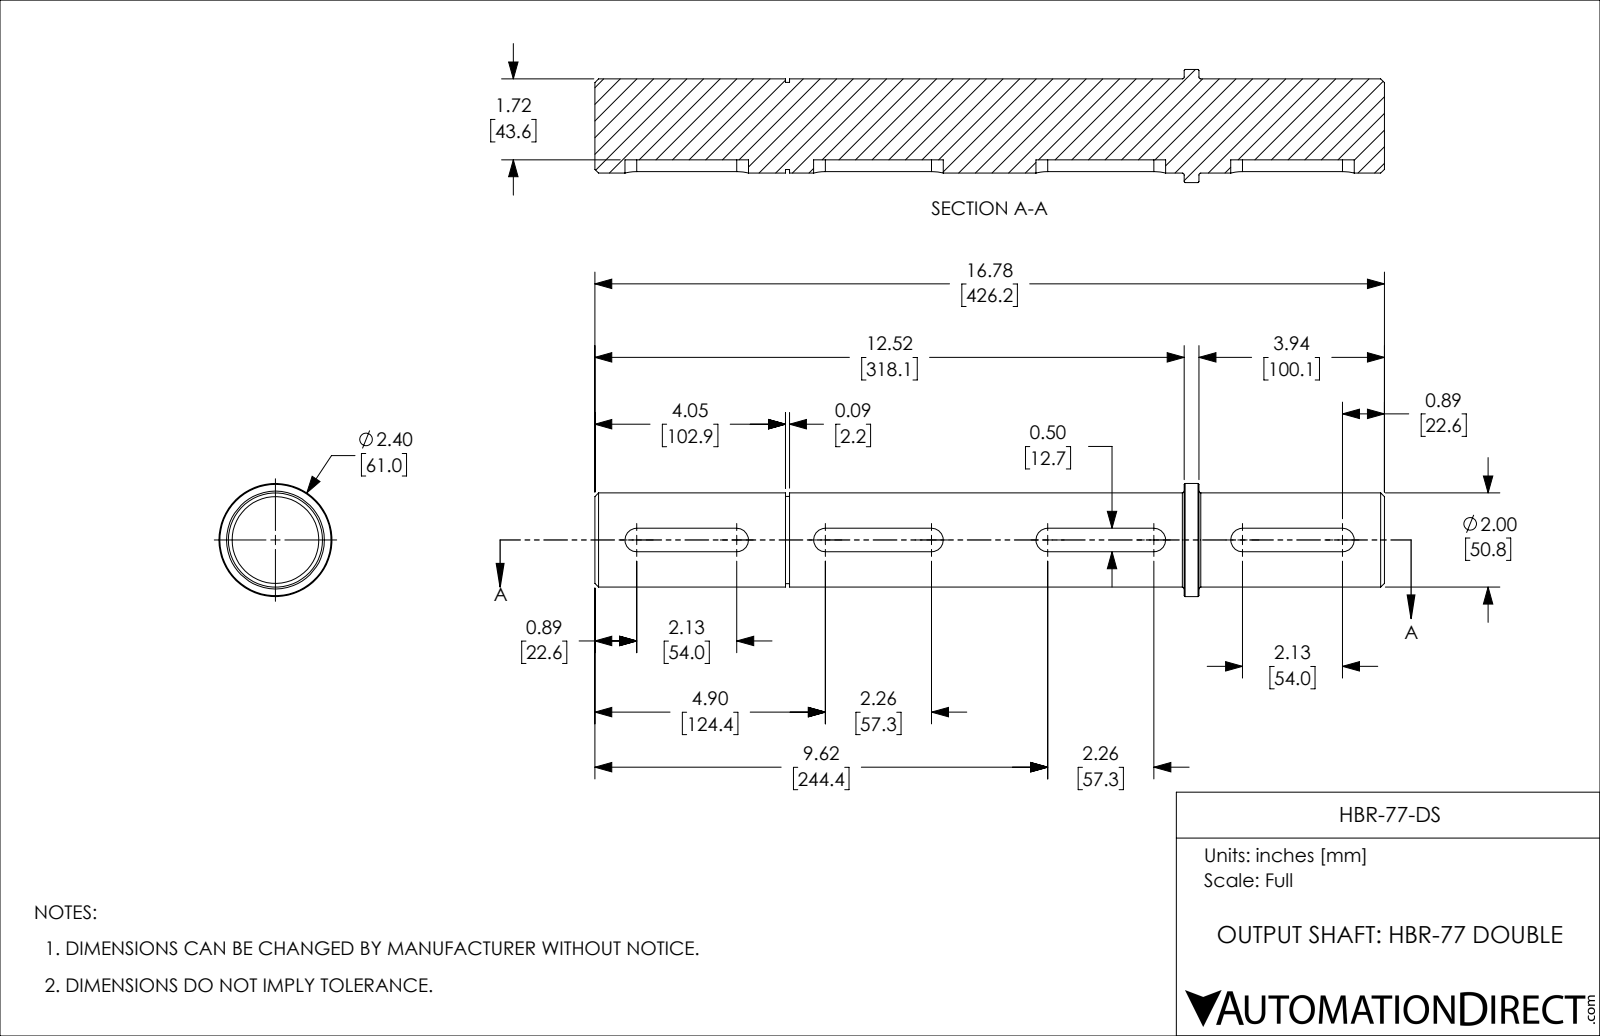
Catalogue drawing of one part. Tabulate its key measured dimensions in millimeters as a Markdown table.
| quantity | value |
| --- | --- |
| part name | HBR-77-DS |
| STEP written by | SolidWorks 2018 (AUTOMOTIVE_DESIGN) |
| units | millimeters |
| bodies | 1 solid, 52 faces (18 planar, 22 cylindrical, 12 other) |
| overall size | 426.2 × 61 × 61 |
| volume | 846 600 mm³ |
| surface area | 77 940 mm² |
| round bosses / shafts (diameter × count) | 61 × 1, 50.8 × 1, 47 × 1 |
| partial cylindrical surfaces (radius × count) | 6.4 × 8 |
| main face-to-face distances | 426.2, 12.7, 318.1, 108.1, 326.1, 8, 100.1, 105.1, 213, 221 |
